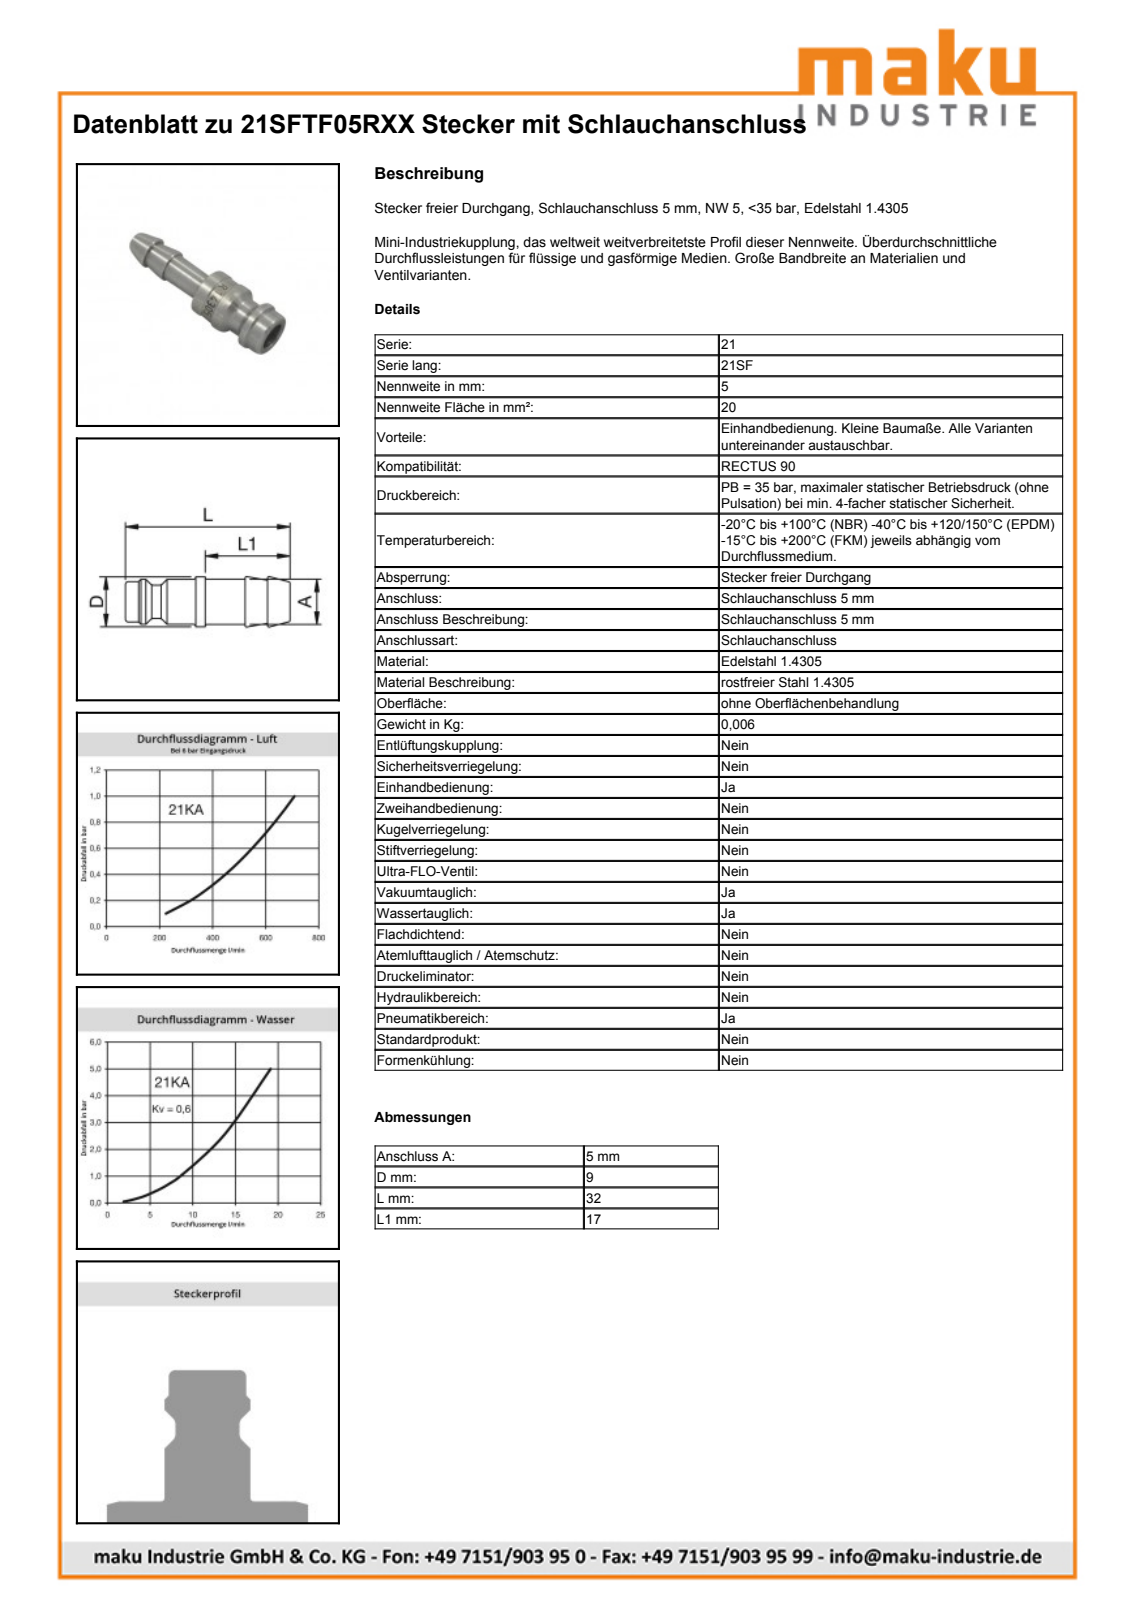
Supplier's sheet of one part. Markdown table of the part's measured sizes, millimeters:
| quantity | value |
| --- | --- |
| part name | D107818 |
| STEP written by | Autodesk Inventor 2013 (AUTOMOTIVE_DESIGN) |
| units | millimeters |
| bodies | 1 solid, 26 faces (5 planar, 7 cylindrical, 14 other) |
| overall size | 32 × 9 × 9 |
| volume | 794 mm³ |
| surface area | 1 170 mm² |
| round holes (diameter × count) | 3 × 1, 4.95 × 1 |
| round bosses / shafts (diameter × count) | 9 × 1, 8.1 × 1, 6.65 × 1, 5.05 × 1 |
| main face-to-face distances | 15, 12.5, 27.5, 4.5, 8, 23, 9, 17, 32 |
